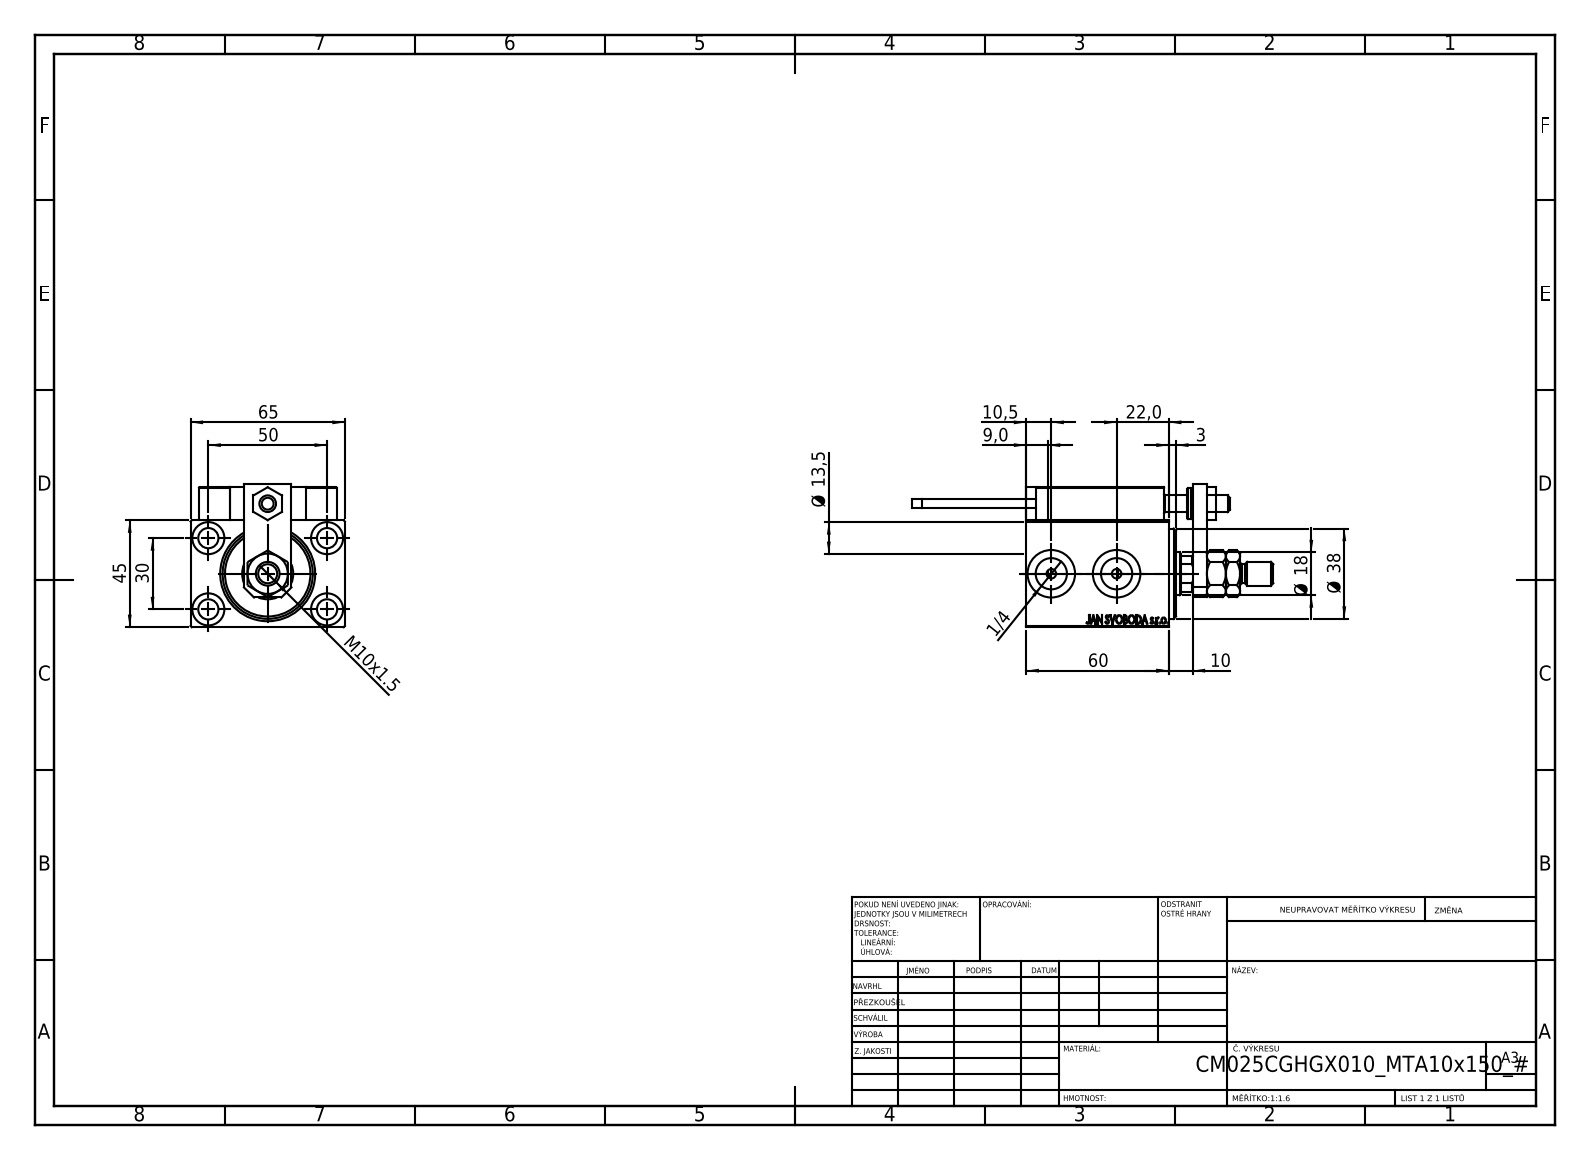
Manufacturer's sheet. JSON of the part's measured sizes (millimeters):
{"part_name": "TYC_L79; NUT_D12; SWITCH DIM B,W; MAGNET (+8 more)", "step_written_by": "SolidWorks 2019 (CONFIG_CONTROL_DESIGN)", "units": "millimeters", "bodies": {"solids": 24, "faces": 1332, "planar": 576, "cylindrical": 192, "other": 564}, "overall_size": [152, 65, 60.5], "volume_mm3": 202222, "surface_area_mm2": 66869, "round_holes": [[4, 6], [8, 5], [8.5, 5], [3.2, 4], [13.5, 4], [5, 2], [13.16, 2], [20, 2], [7, 1], [14.5, 1], [18, 1], [21.5, 1]], "round_bosses_or_shafts": [[5, 2], [3.8, 2], [13, 1], [11, 1], [10, 1], [8, 1]], "partial_cylinders_radius": [[0.3, 30], [3, 2], [8.5, 1]], "face_to_face_distances": [45, 10, 7, 14, 59, 6, 3, 13, 65, 3.5], "hole_center_spacings": [29.15, 11.37, 12.17, 20, 25.06, 28.9, 29.59, 29.69]}
